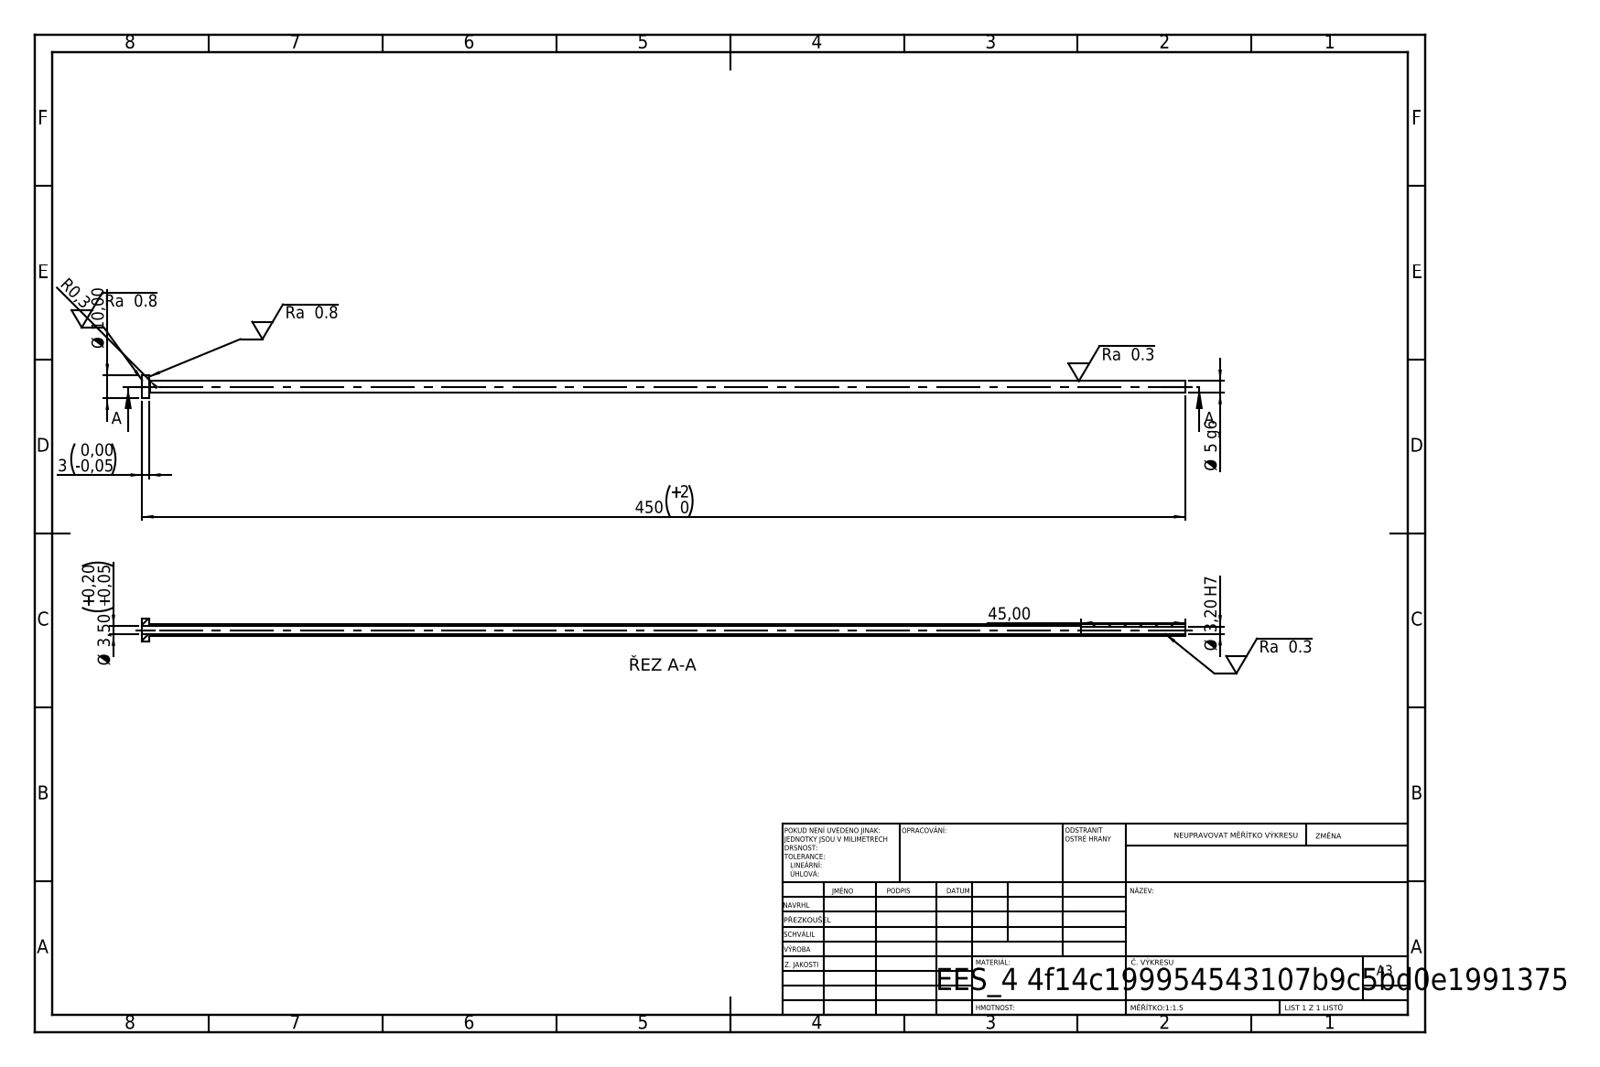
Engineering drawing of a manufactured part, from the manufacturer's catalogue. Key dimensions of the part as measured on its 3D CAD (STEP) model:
STEP written by: SolidWorks 2019 (CONFIG_CONTROL_DESIGN)
Units: millimetres
Bodies: 1 solid, 14 faces (4 planar, 8 cylindrical, 2 other)
Overall size (bounding box): 450 × 10 × 10
Volume: 4 754 mm³ · Surface area: 12 160 mm²
Round holes (diameter × count): ⌀3.2 ×1, ⌀3.5 ×1
Round bosses / shafts (diameter × count): ⌀10 ×1, ⌀5 ×1
Main face-to-face distances: 3, 450, 447, 405, 402, 45
